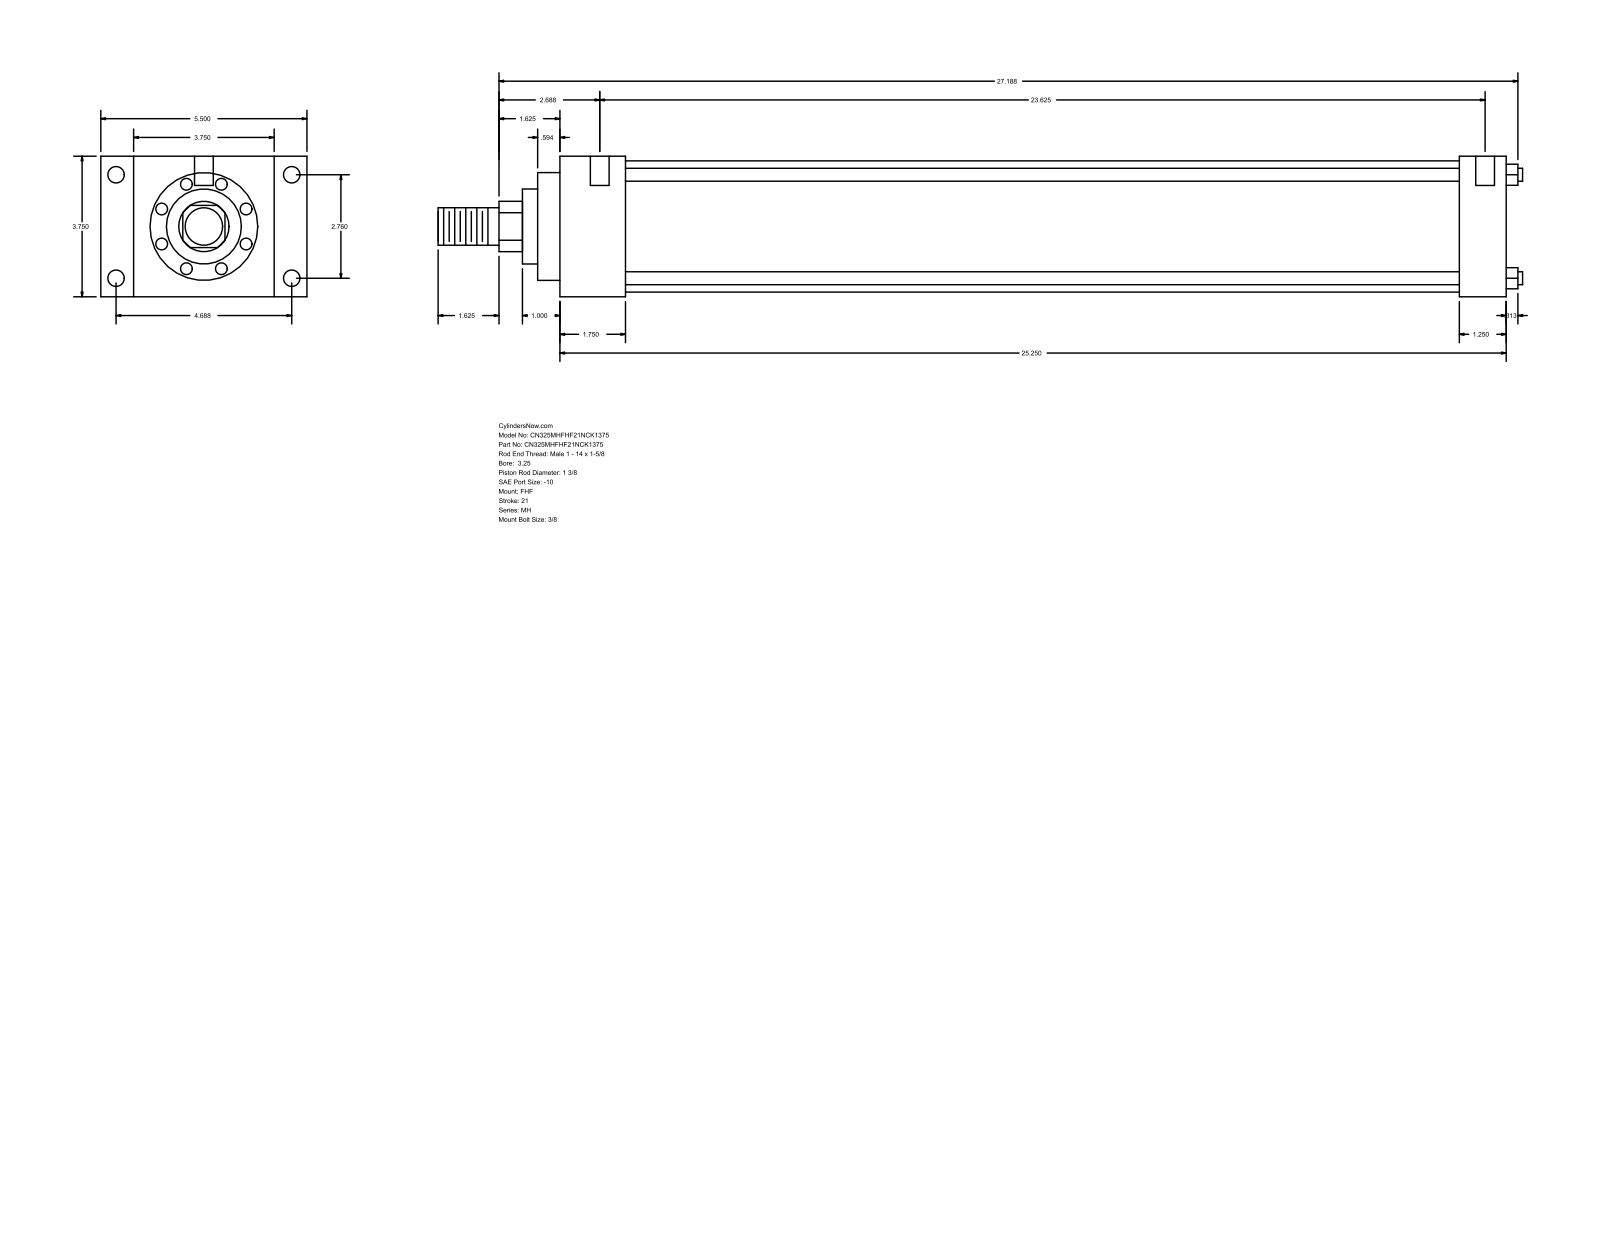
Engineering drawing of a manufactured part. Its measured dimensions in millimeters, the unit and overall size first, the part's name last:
Units: millimetres
Overall size (bounding box): 735.01 × 139.7 × 95.25
Round holes (diameter × count): ⌀5.56 ×4, ⌀11.13 ×4, ⌀12.7 ×2
Round bosses / shafts (diameter × count): ⌀8.76 ×4, ⌀88.9 ×1, ⌀73.03 ×1, ⌀50.8 ×1, ⌀34.92 ×1, ⌀25.4 ×1
Partial cylindrical surfaces — rounded edges, fillets, slot ends (radius × count): R17.06 ×1
Main face-to-face distances: 95.24, 641.35, 44.45, 596.9, 22.23, 117.47, 139.7, 609.61, 565.16, 31.74
Hole centre spacings: 70.1, 119.06, 138.16, 606.43, 1.59, 4.76, 600.08, 601.67
Bodies: 0 solids, 90 faces (61 planar, 29 cylindrical, 0 other)
Part name (STEP PRODUCT): MH_FHF__0325_1.375
STEP written by: GSSL Pune (CONFIG_CONTROL_DESIGN)
